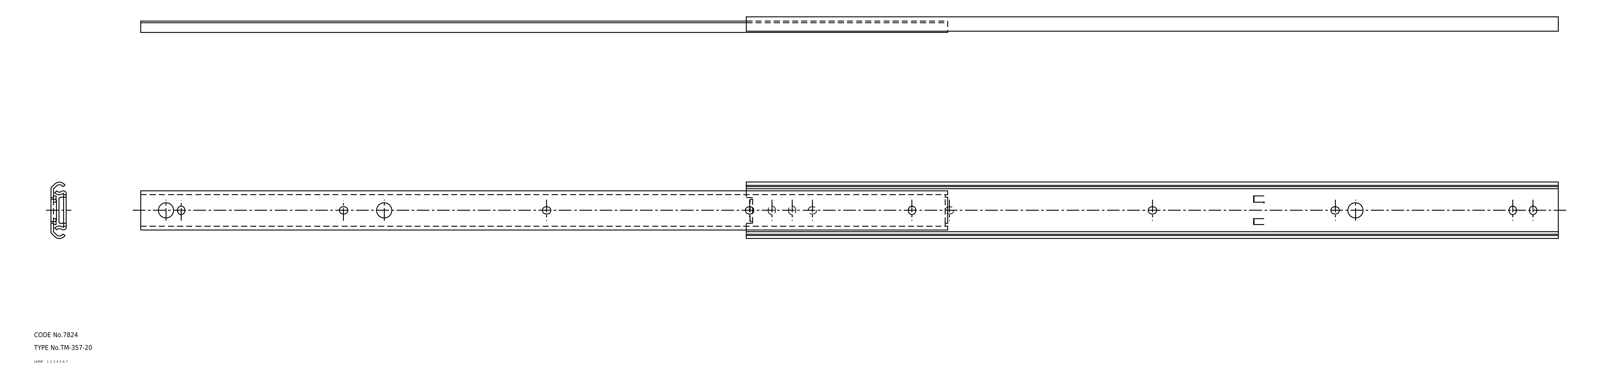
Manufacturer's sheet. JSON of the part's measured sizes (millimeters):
{"part_name": "member_B; member_A; TM_357_20", "step_written_by": "SolidWorks 2015 (AUTOMOTIVE_DESIGN)", "units": "millimeters", "bodies": {"solids": 2, "faces": 121, "planar": 62, "cylindrical": 59, "other": 0}, "overall_size": [887, 35.3, 9.6], "volume_mm3": 64123, "surface_area_mm2": 84159, "round_holes": [[9.5, 3]], "partial_cylinders_radius": [[2.25, 26], [1, 4], [1.6, 4], [0.2, 2], [1.8, 2], [2.4, 2], [2.5, 2], [4, 2]], "face_to_face_distances": [1.6, 8, 9.6, 6.4, 382, 4.5, 122.2, 505, 887, 503.4], "hole_center_spacings": [136.5, 607.6, 744.1]}
